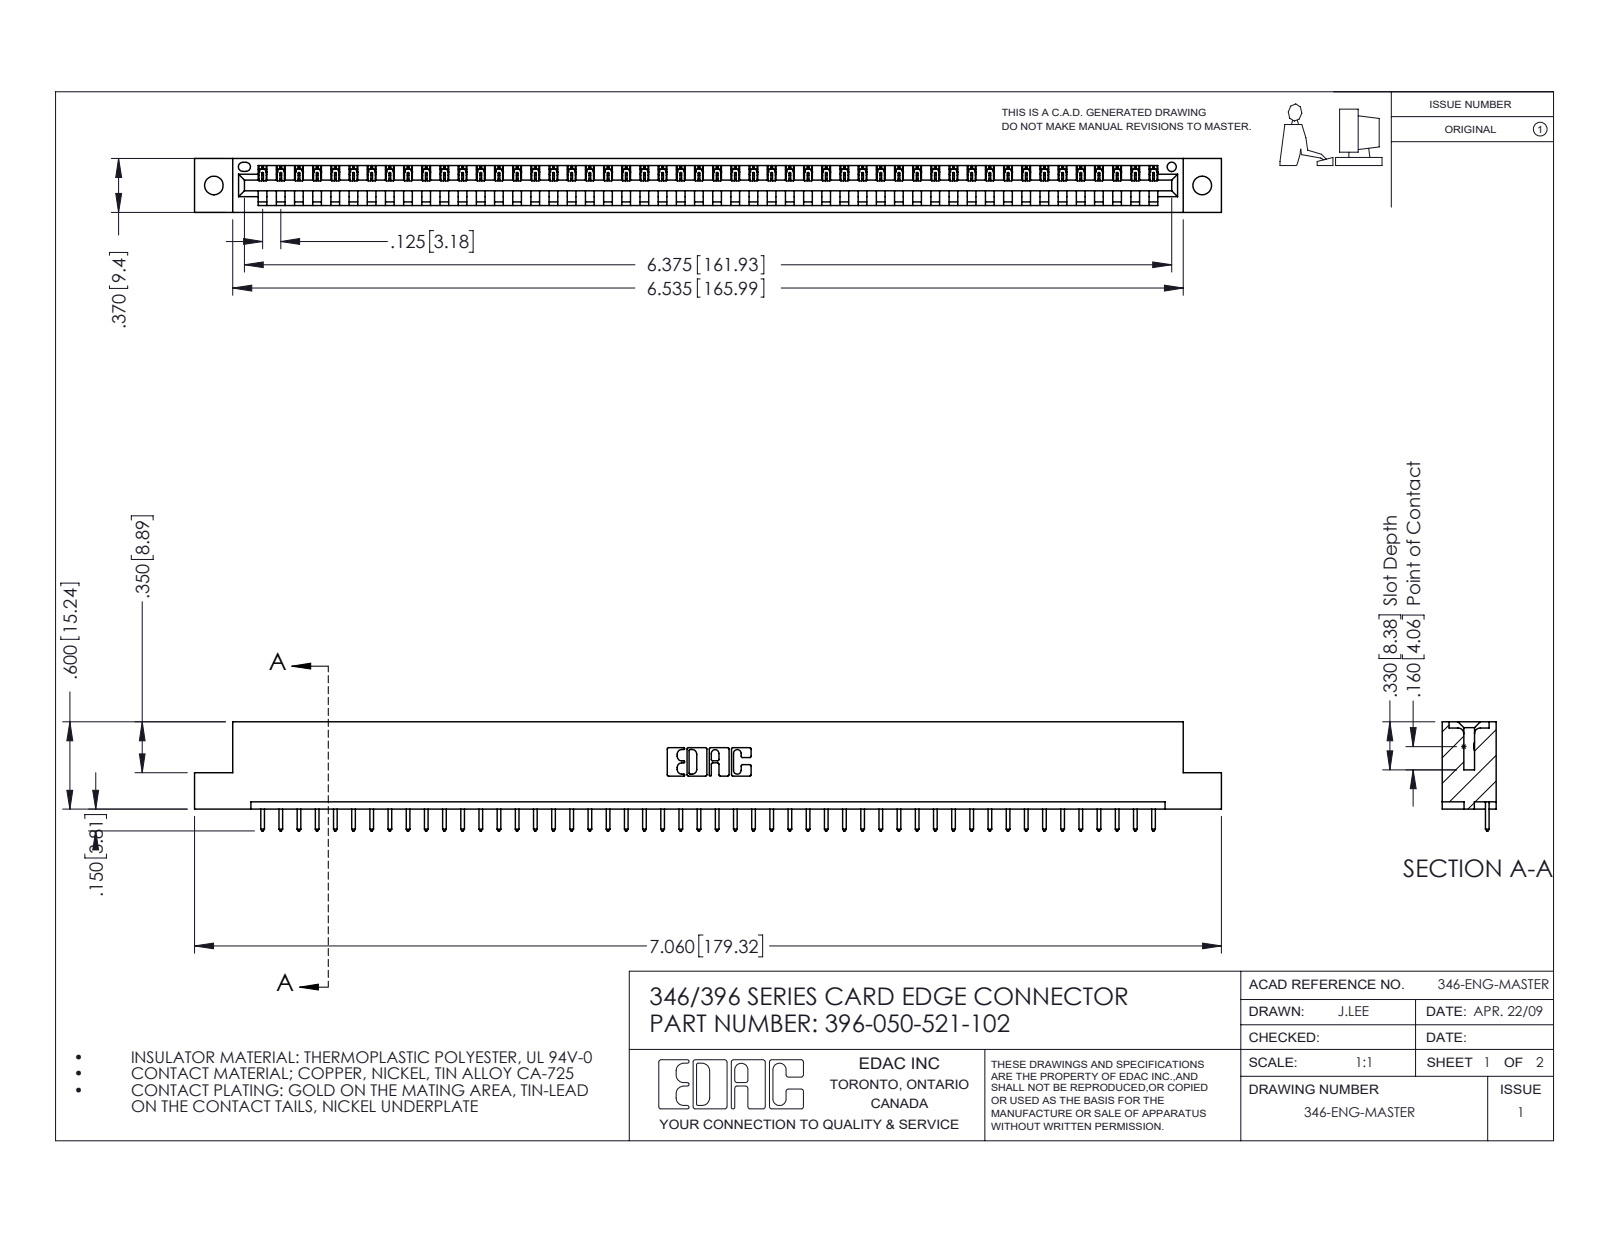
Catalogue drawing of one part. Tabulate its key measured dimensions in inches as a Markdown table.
| quantity | value |
| --- | --- |
| part name | 396-050-521-102; 345-292-001_345-293-121; 346 Part_Flush Mounting Lugs - 0.128 Dia |
| STEP written by | SolidWorks 2016 (CONFIG_CONTROL_DESIGN) |
| units | inches |
| bodies | 51 solids, 3022 faces (2076 planar, 946 cylindrical, 0 other) |
| overall size | 7.06 × 0.75 × 0.37 |
| volume | 1.04 in³ |
| surface area | 31.85 in² |
| round holes (diameter × count) | 0.128 × 2, 0.064 × 1 |
| partial cylindrical surfaces (radius × count) | 0.006 × 100, 0.01 × 100, 0.01 × 22, 0.007 × 6, 0.031 × 6, 0.026 × 3, 0.031 × 2, 0.04 × 2 |
| main face-to-face distances | 0.048, 0.322, 0.37, 0.25, 0.072, 0.298, 0.025, 0.148, 0.222, 0.1 |
| hole center spacings | 0.246, 6.586, 6.795 |
